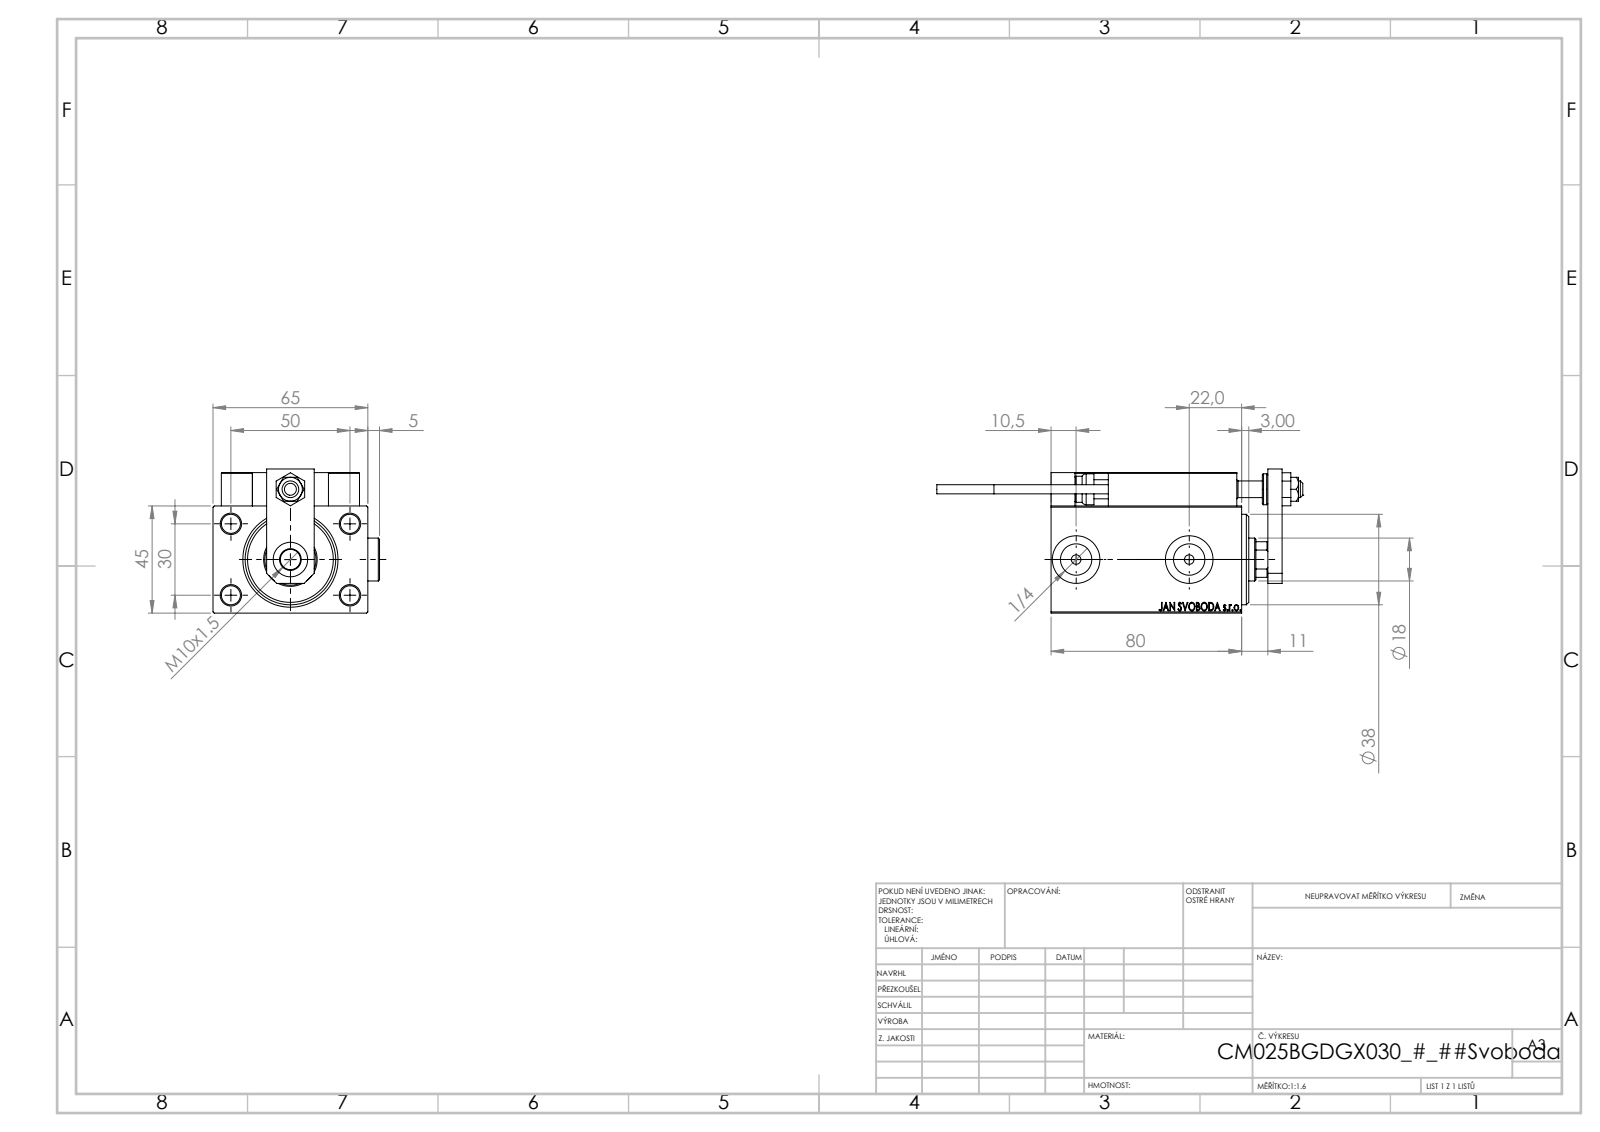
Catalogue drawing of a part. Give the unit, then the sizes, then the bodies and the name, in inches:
Units: inches
Overall size (bounding box): 6.051 × 2.752 × 2.382
Round holes (diameter × count): ⌀0.315 ×9, ⌀0.157 ×6, ⌀0.126 ×4, ⌀0.197 ×2, ⌀0.518 ×2, ⌀0.787 ×2, ⌀0.276 ×1, ⌀0.335 ×1, ⌀0.571 ×1, ⌀0.709 ×1, ⌀0.846 ×1, ⌀0.886 ×1
Round bosses / shafts (diameter × count): ⌀0.709 ×2, ⌀0.197 ×2, ⌀0.15 ×2, ⌀0.512 ×1, ⌀0.433 ×1
Partial cylindrical surfaces — rounded edges, fillets, slot ends (radius × count): R0.012 ×30, R0.118 ×2, R0.335 ×1
Main face-to-face distances: 1.772, 0.551, 2.559, 0.236, 2.323, 0.197, 0.512, 0.138, 3.583, 0.748
Hole centre spacings: 1.148, 0.448, 0.787, 1.138, 1.165, 1.169, 1.181, 1.262
Volume: 16.16 in³ · Surface area: 110.1 in²
Bodies: 26 solids, 1372 faces (595 planar, 200 cylindrical, 577 other)
Part name (STEP PRODUCT): KONCOVKA; V450CM_VC_B; TYC_L79; SWITCH_X_FRONT_BACK (+7 more)
STEP written by: SolidWorks 2019 (CONFIG_CONTROL_DESIGN)
